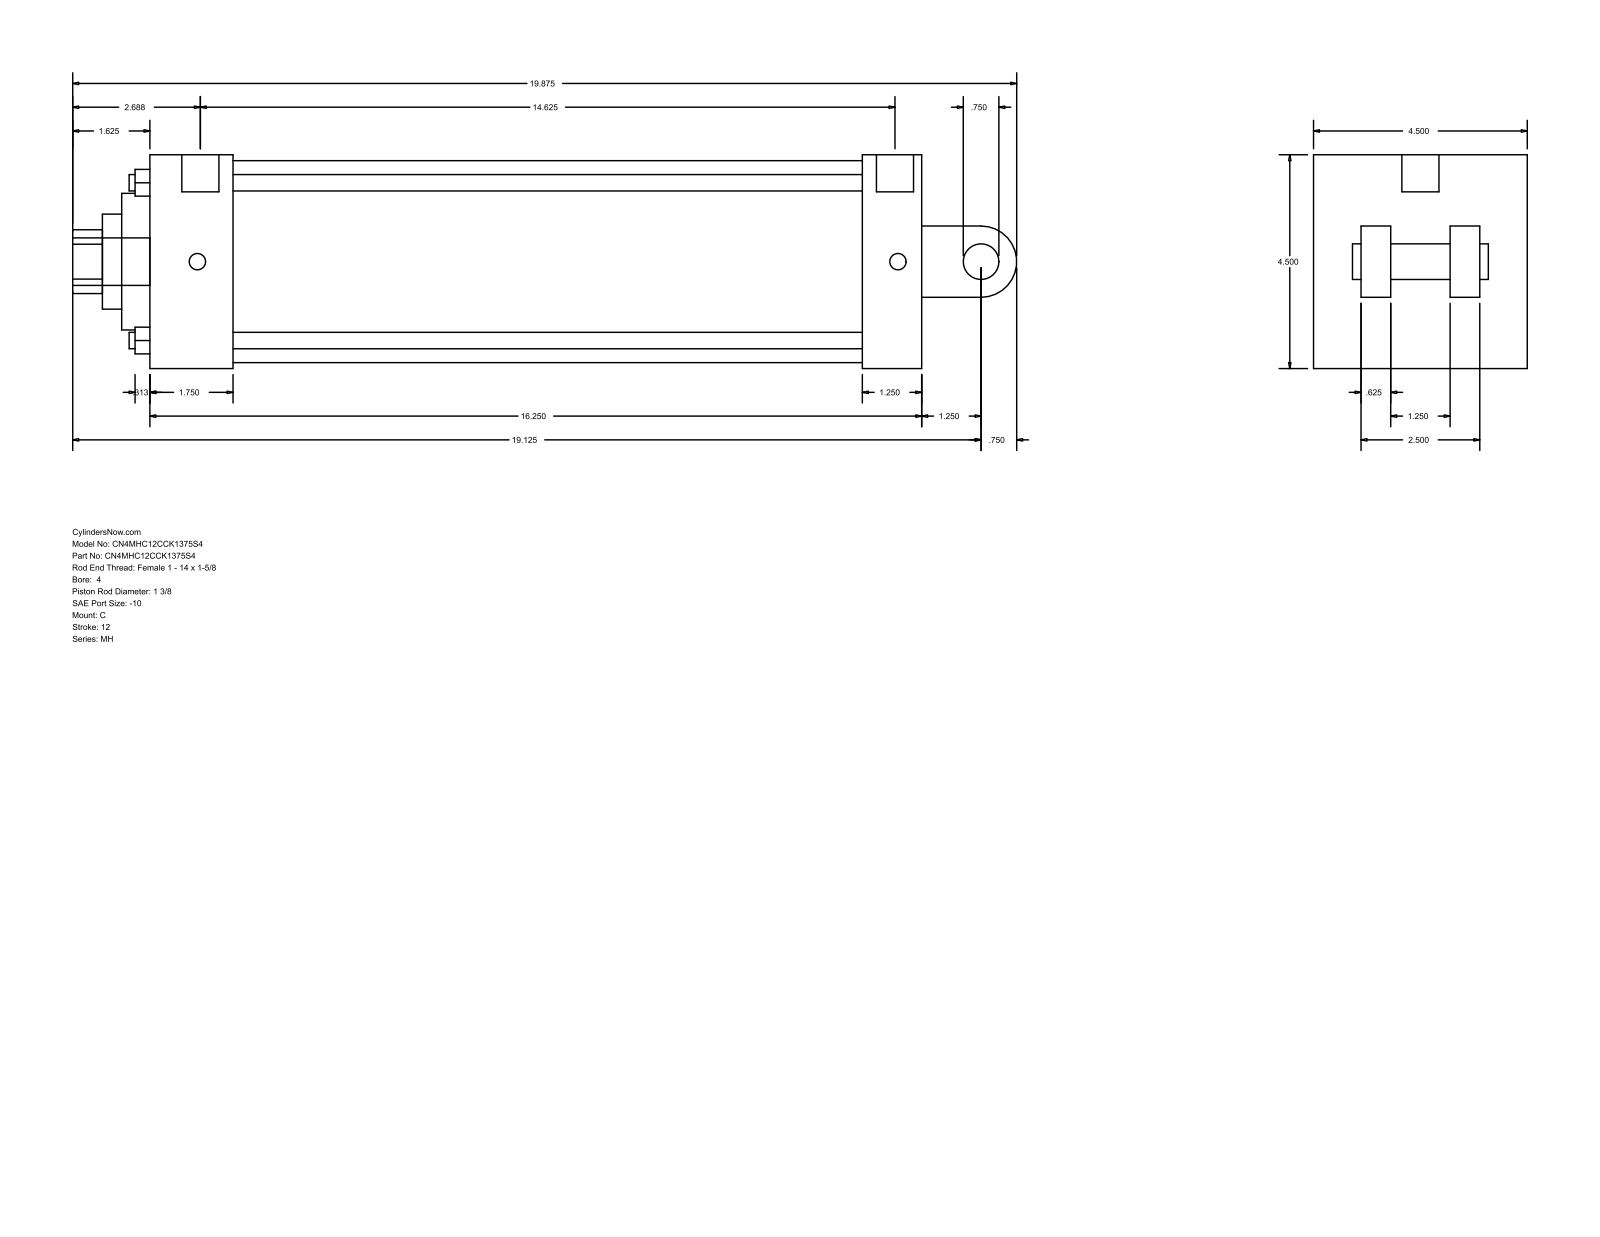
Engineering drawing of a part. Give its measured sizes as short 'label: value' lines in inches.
name: MH_C__0400_1.375
written by: GSSL Pune (CONFIG_CONTROL_DESIGN)
unit: in
bodies: 0 solids, 101 faces (71 planar, 30 cylindrical, 0 other)
size: 19.875 × 4.5 × 4.5
holes: 4× ⌀0.345, 2× ⌀0.344, 1× ⌀0.781, 1× ⌀1.375, 1× ⌀2, 1× ⌀2.875, 1× ⌀4.25
bosses: 2× ⌀0.344, 1× ⌀1, 1× ⌀0.781, 1× ⌀0.75
rounds: 1× R0.672, 1× R0.75
face distances: 4.5, 16.25, 1.75, 15, 13.25, 14.5, 1.25, 2.875, 1.625, 1.5
hole spacings: 2.347, 3.32, 4.695, 0.062
